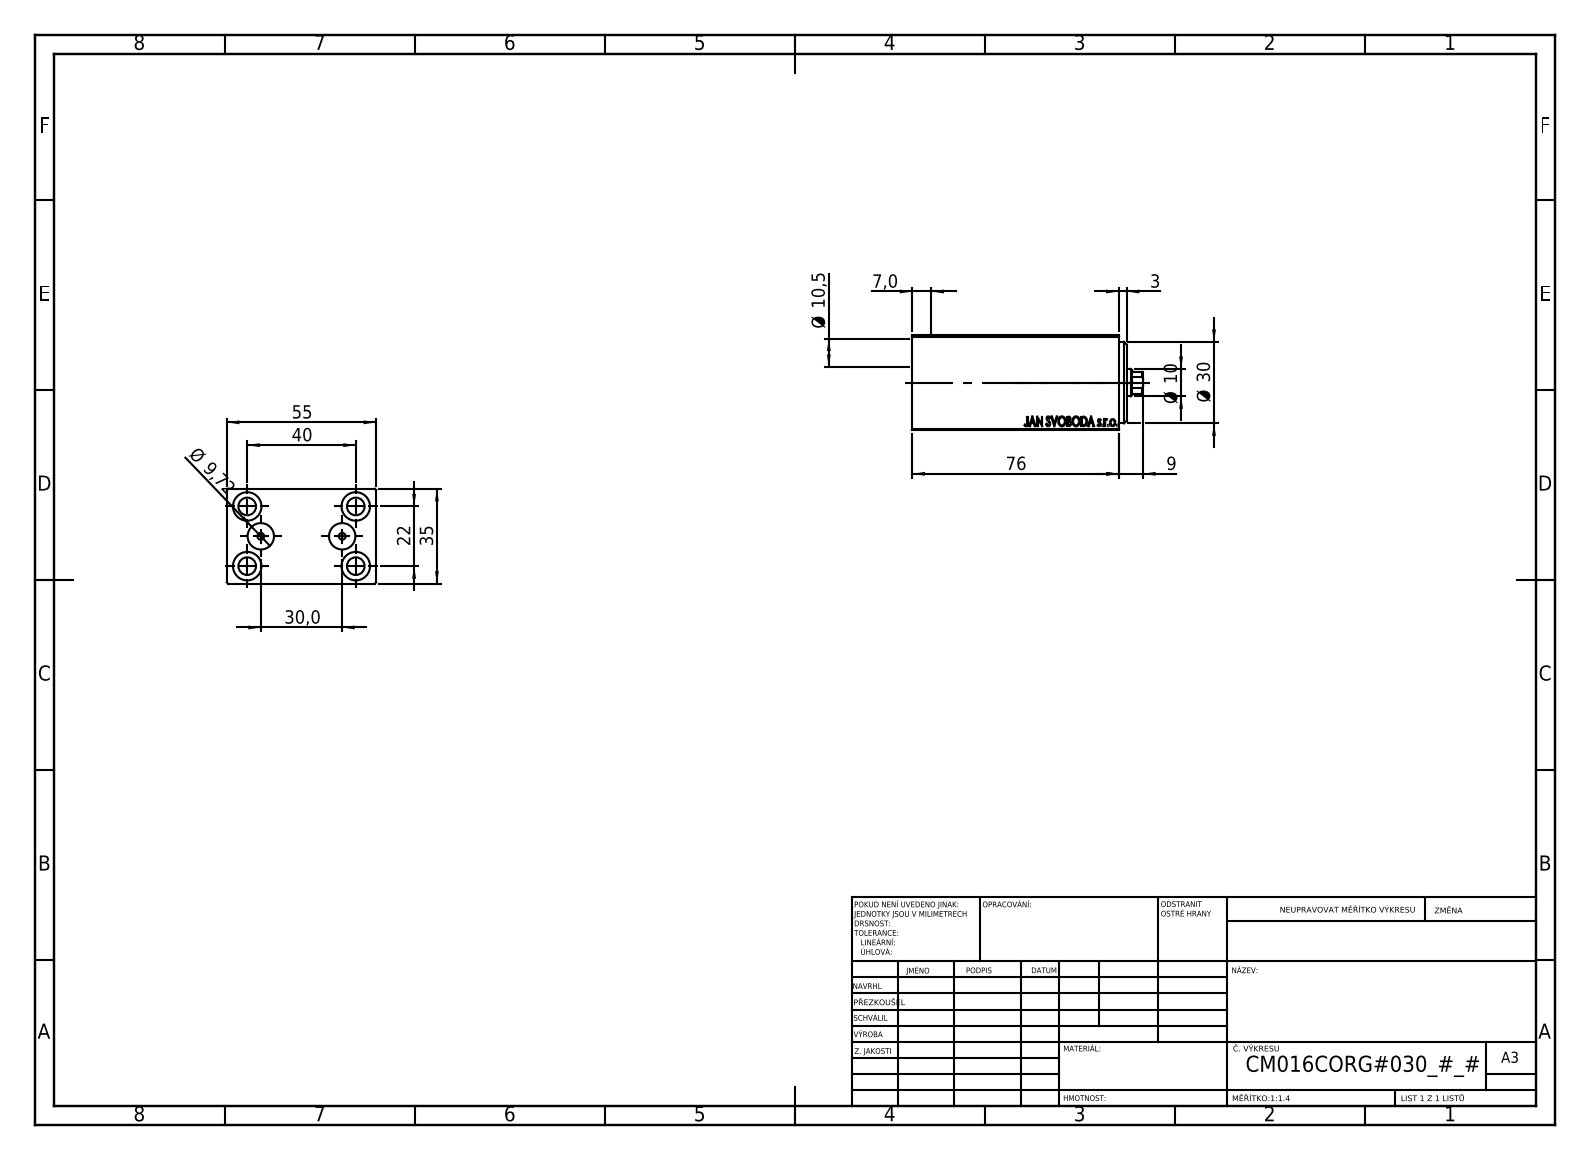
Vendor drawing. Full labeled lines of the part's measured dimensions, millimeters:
Part name (STEP PRODUCT): V450CM_C_VCP; V450CM_C_Body; V450CM_VC_B
STEP written by: SolidWorks 2019 (CONFIG_CONTROL_DESIGN)
Units: millimetres
Bodies: 3 solids, 861 faces (409 planar, 58 cylindrical, 394 other)
Overall size (bounding box): 85 × 55 × 35
Volume: 129 524 mm³ · Surface area: 35 779 mm²
Round holes (diameter × count): ⌀6.5 ×4, ⌀10.5 ×4, ⌀2.5 ×2, ⌀9.72 ×2, ⌀4.5 ×1, ⌀10 ×1, ⌀13.5 ×1, ⌀14.5 ×1, ⌀16 ×1, ⌀18 ×1, ⌀30 ×1
Partial cylindrical surfaces — rounded edges, fillets, slot ends (radius × count): R4.5 ×1
Main face-to-face distances: 35, 55, 5, 71, 76, 2, 3, 69, 66, 8
Hole centre spacings: 12.08, 22.83, 36.69, 15, 22, 40, 45.65, 30
